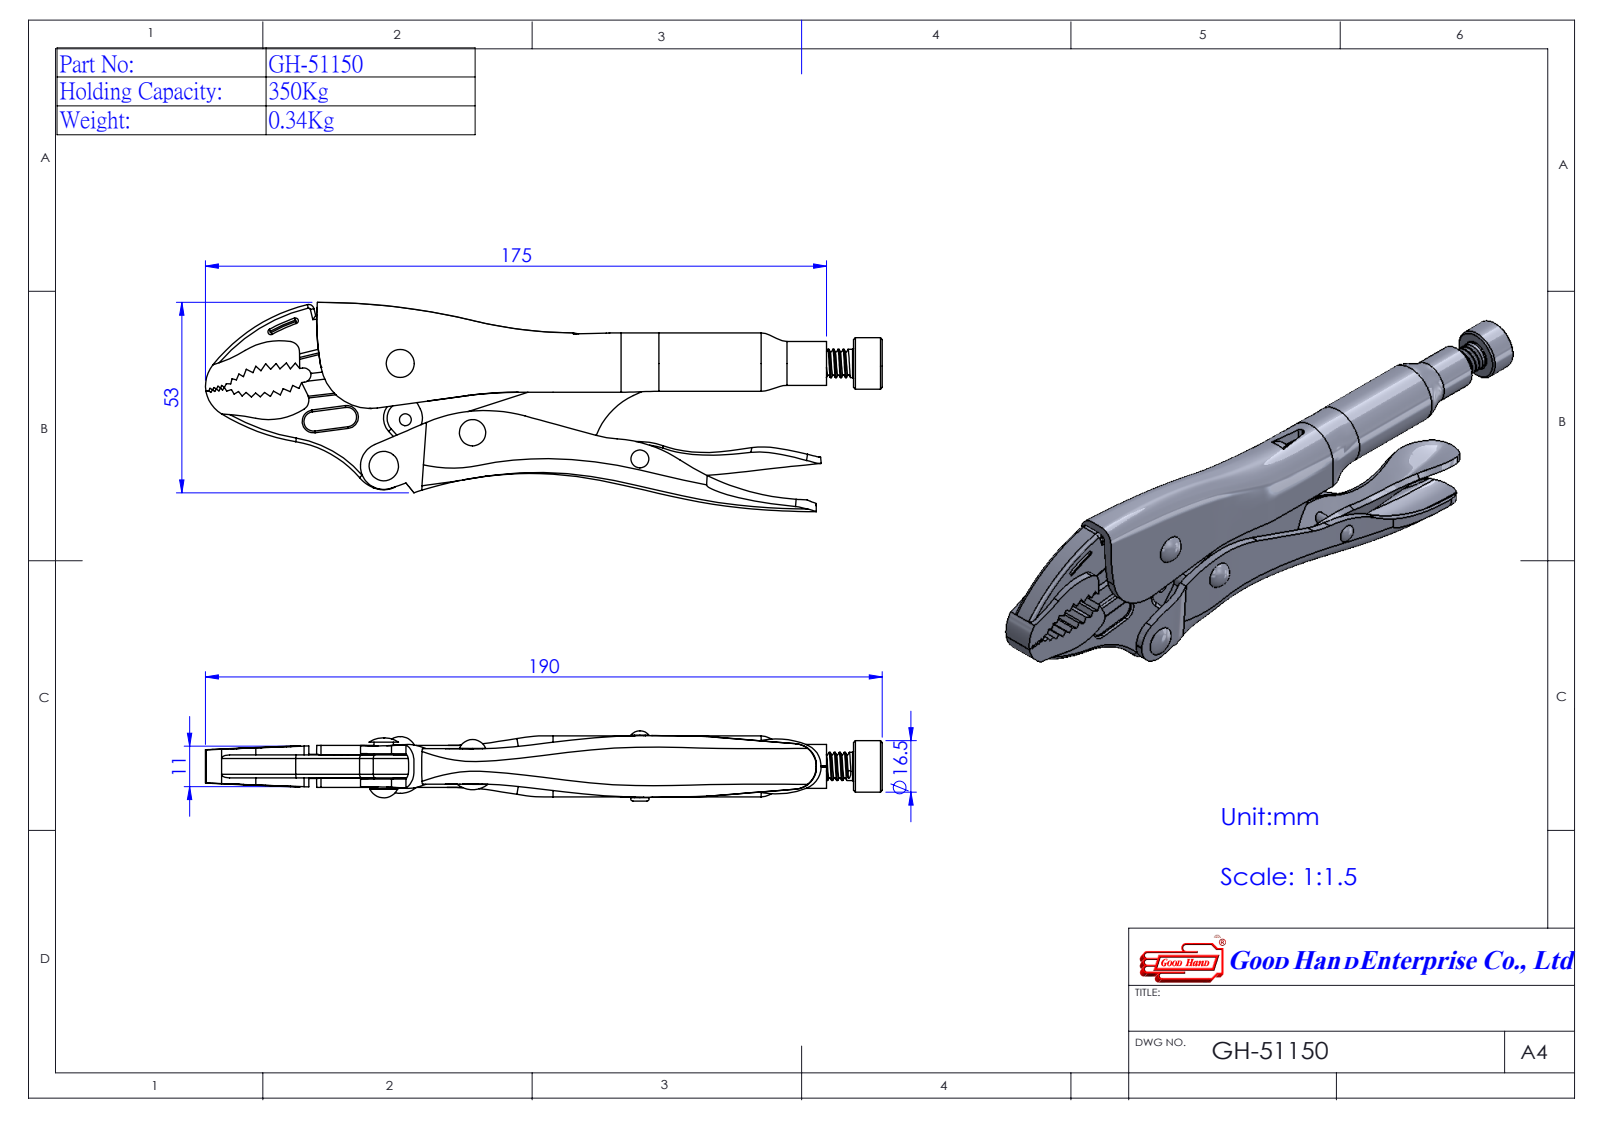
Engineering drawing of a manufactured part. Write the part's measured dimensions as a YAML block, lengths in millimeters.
part_name: "GH-51150(簡化); Group1^GH-51150(簡化)"
step_written_by: "SolidWorks 2016 (AUTOMOTIVE_DESIGN)"
units: millimeters
bodies: {solids: 12, faces: 623, planar: 151, cylindrical: 243, other: 229}
overall_size: [187.88, 58.06, 19.55]
volume: 46219
surface_area: 37079
round_holes:
  - {diameter: 5.6, count: 3}
  - {diameter: 3.2, count: 1}
  - {diameter: 3.3, count: 1}
  - {diameter: 5.5, count: 1}
  - {diameter: 7, count: 1}
  - {diameter: 11.8, count: 1}
round_bosses_or_shafts:
  - {diameter: 5.4, count: 3}
  - {diameter: 1.2, count: 3}
  - {diameter: 17, count: 1}
  - {diameter: 14.3, count: 1}
  - {diameter: 12.2, count: 1}
  - {diameter: 7.85, count: 1}
  - {diameter: 5.45, count: 1}
  - {diameter: 2.95, count: 1}
partial_cylinders:
  - {radius: 1, count: 21}
  - {radius: 0.5, count: 10}
  - {radius: 3, count: 5}
  - {radius: 1.5, count: 3}
  - {radius: 0.8, count: 2}
  - {radius: 2, count: 2}
  - {radius: 2.13, count: 2}
  - {radius: 2.7, count: 2}
face_to_face_distances: [0.9, 5.5, 4.6, 6.4, 1.05, 5.65, 6.55, 6.7, 3.7, 1.8]
hole_center_spacings: [14.23, 15.73, 19.03, 26.4, 27.84, 28.92, 47.18, 66.2]
